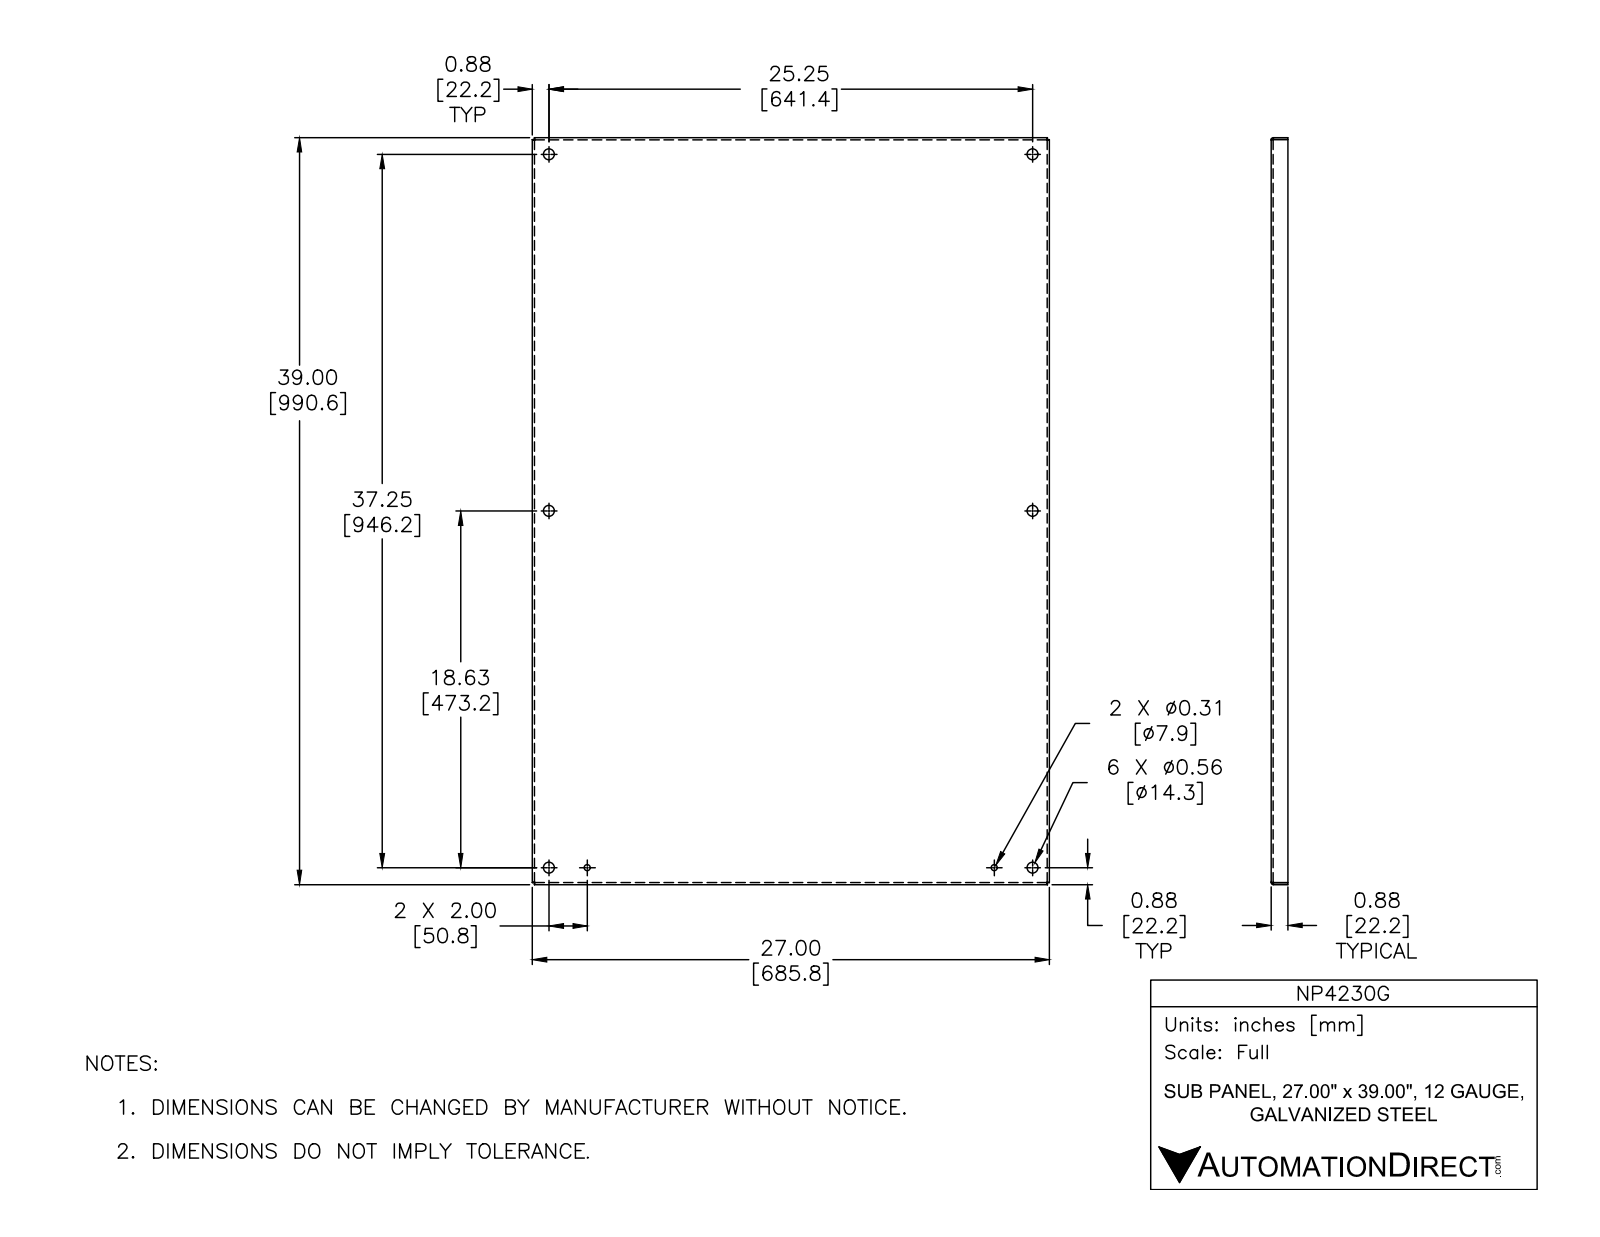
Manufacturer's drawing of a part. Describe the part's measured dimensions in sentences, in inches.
The part is named "NP4230G". Its 3-D file was written by "Autodesk Inventor 2012 (AUTOMOTIVE_DESIGN)". It is 1 solid with 46 faces: 22 planar, 16 cylindrical and 8 other. Overall it measures 39 by 27 by 0.875 inches. Its volume is 107.7 cubic inches and its surface area 2 313 square inches. Round holes: 6 of diameter 0.563, 2 of diameter 0.312. Partial cylindrical surfaces (rounded edges, fillets, slot ends): 4 of radius 0.031, 4 of radius 0.125. The main face-to-face distances are 0.094, 26.906, 38.906, 27, 26.813, 39, 38.813, 0.781, 0.875, 0.105. The hole center spacings are 18.625, 18.625, 18.732, 25.25, 31.376, 31.376, 37.25, 37.304.
